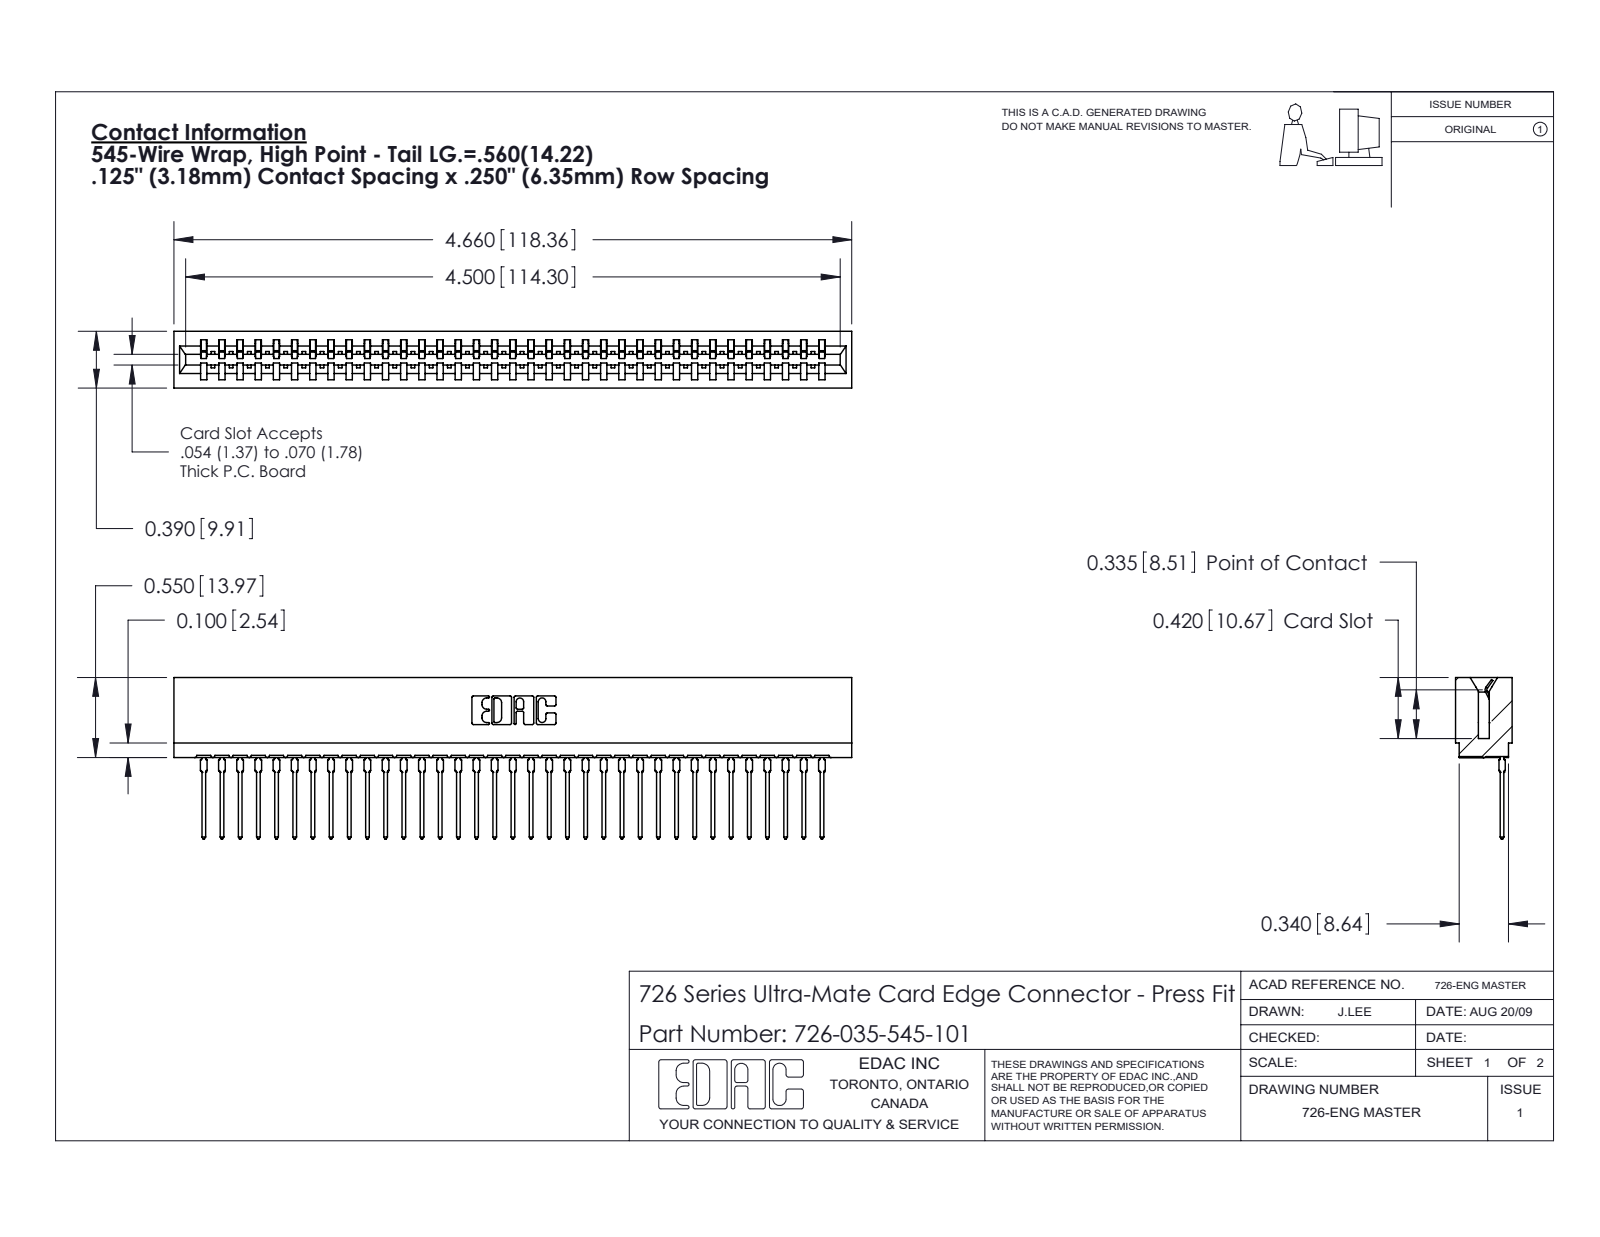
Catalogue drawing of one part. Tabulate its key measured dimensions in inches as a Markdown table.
| quantity | value |
| --- | --- |
| part name | 726 Part_.515 Slot Depth - 01; 726-035-545-101; 746-292-001_545 |
| STEP written by | SolidWorks 2020 (CONFIG_CONTROL_DESIGN) |
| units | inches |
| bodies | 36 solids, 3877 faces (2260 planar, 707 cylindrical, 910 other) |
| overall size | 4.66 × 1.109 × 0.39 |
| volume | 0.653 in³ |
| surface area | 25.92 in² |
| partial cylindrical surfaces (radius × count) | 0.021 × 70, 0.015 × 36, 0.01 × 22, 0.007 × 6, 0.031 × 6, 0.005 × 4, 0.011 × 4, 0.026 × 3 |
| main face-to-face distances | 0.057, 0.333, 0.39, 0.25, 0.025, 0.307, 0.083, 0.5, 0.275, 0.365 |
